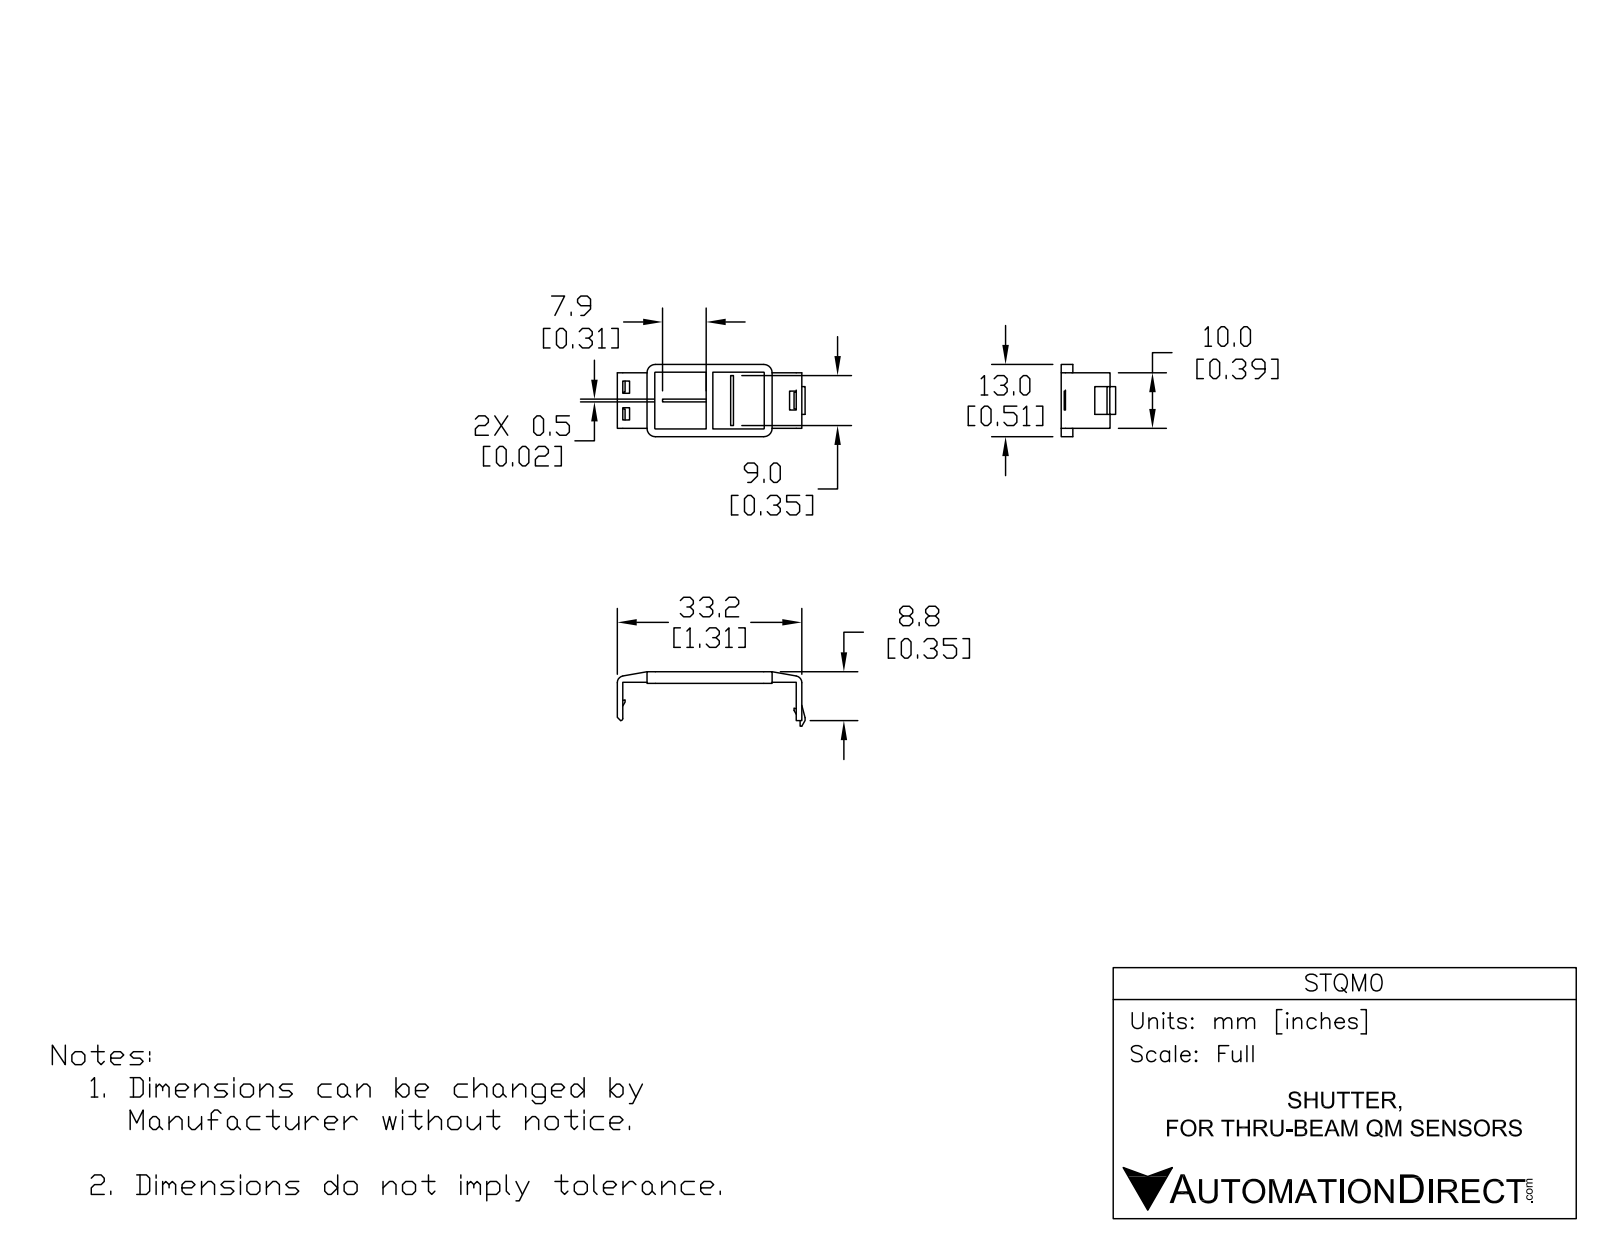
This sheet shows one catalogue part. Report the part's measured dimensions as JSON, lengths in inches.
{"part_name": "stqm0", "step_written_by": "SolidWorks 2017 (AUTOMOTIVE_DESIGN)", "units": "inches", "bodies": {"solids": 1, "faces": 110, "planar": 80, "cylindrical": 23, "other": 7}, "overall_size": [1.331, 0.512, 0.386], "volume_in3": 0.025, "surface_area_in2": 1.621, "partial_cylinders_radius": [[0.004, 4], [0.016, 4], [0.024, 4], [0.059, 4], [0.047, 2]], "face_to_face_distances": [0.039, 1.268, 0.059, 0.083, 0.413, 0.453, 0.016, 1.228, 1.307, 0.02]}
